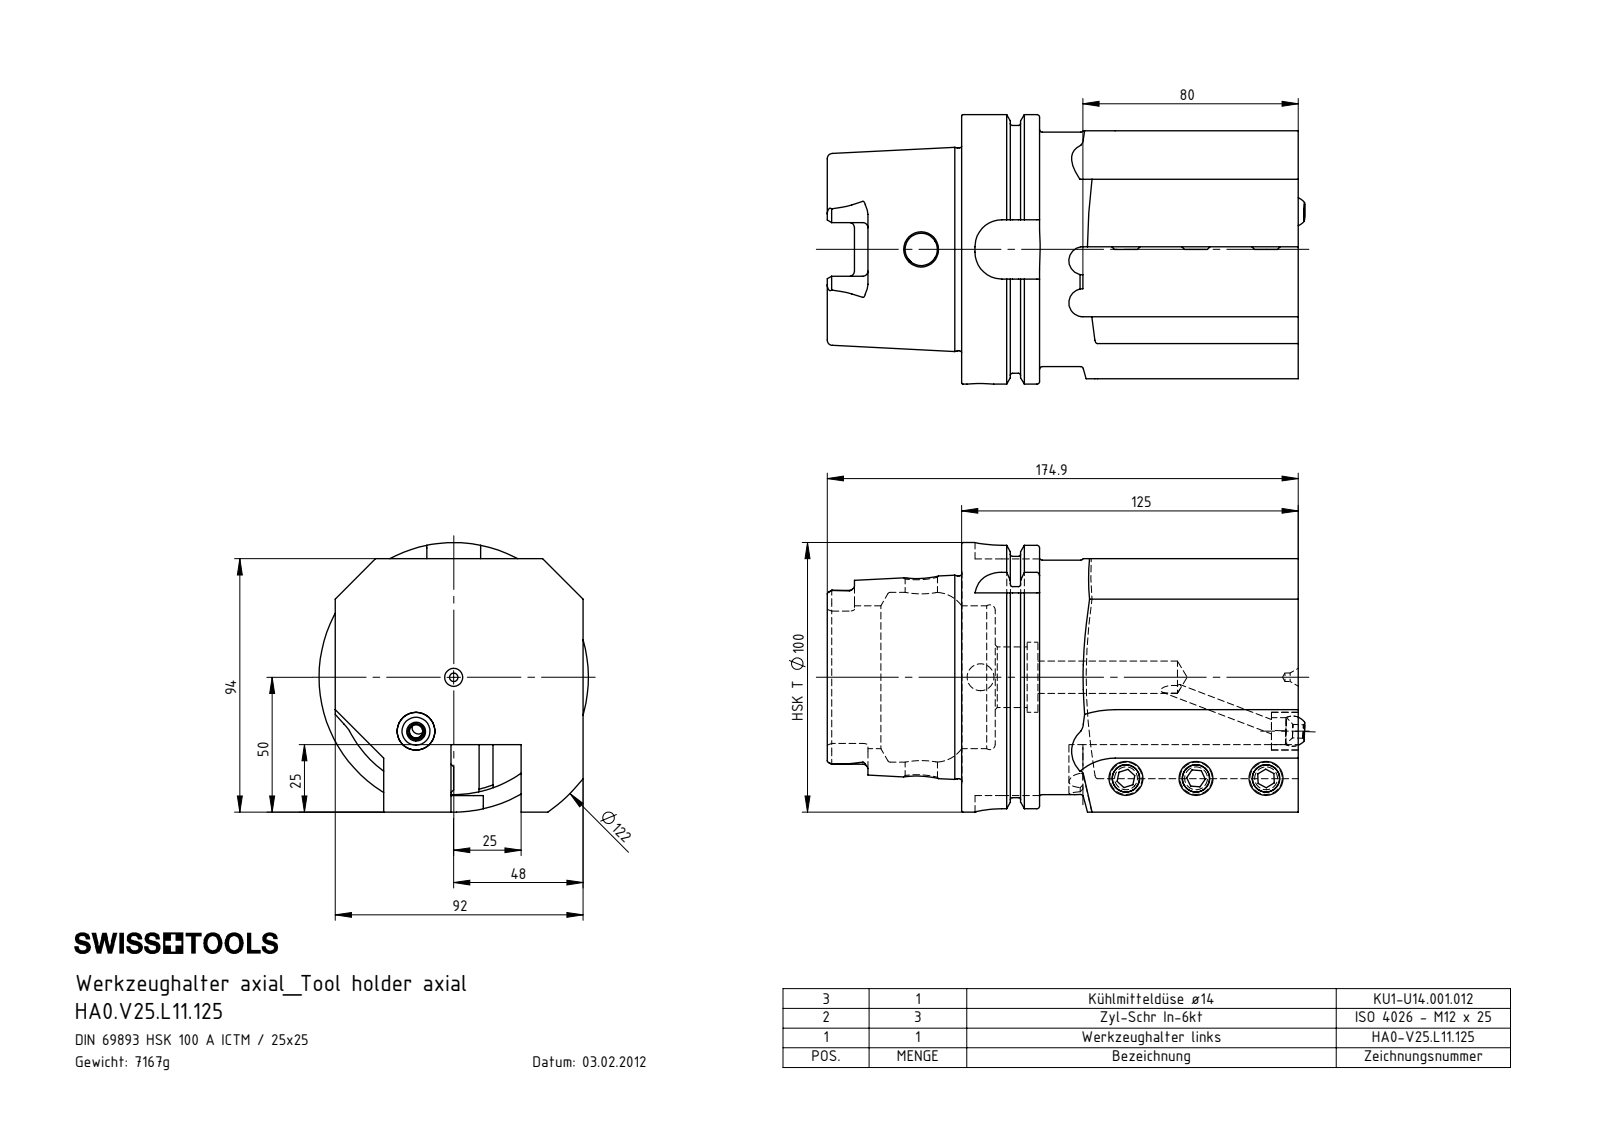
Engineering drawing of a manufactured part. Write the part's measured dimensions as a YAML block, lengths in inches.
part_name: "HA0.V25.L11.125; KU1-U14.001.012_1; KU1-U14.001.012; KU1-U14.001.012_2 (+2 more)"
step_written_by: "SolidWorks 2017 (AUTOMOTIVE_DESIGN)"
units: inches
bodies: {solids: 6, faces: 199, planar: 82, cylindrical: 47, other: 70}
overall_size: [6.996, 3.937, 3.937]
volume: 55.76
surface_area: 151.4
round_holes:
  - {diameter: 0.402, count: 3}
  - {diameter: 0.197, count: 2}
  - {diameter: 0.394, count: 2}
  - {diameter: 0.472, count: 2}
  - {diameter: 0.124, count: 1}
  - {diameter: 0.551, count: 1}
  - {diameter: 0.886, count: 1}
  - {diameter: 1.024, count: 1}
  - {diameter: 2.087, count: 1}
  - {diameter: 2.48, count: 1}
round_bosses_or_shafts:
  - {diameter: 0.472, count: 3}
  - {diameter: 3.937, count: 1}
  - {diameter: 3.62, count: 1}
  - {diameter: 3.425, count: 1}
  - {diameter: 2.963, count: 1}
partial_cylinders:
  - {radius: 0.075, count: 6}
  - {radius: 0.192, count: 4}
  - {radius: 0.394, count: 4}
  - {radius: 0.205, count: 2}
  - {radius: 2.402, count: 1}
face_to_face_distances: [2.717, 0.984, 3.622, 4.921, 3.701, 0.906, 1.024, 3.702, 1.929, 1.693]
hole_center_spacings: [1.024, 0.961, 2.047, 2.588, 3.478, 4.427]
